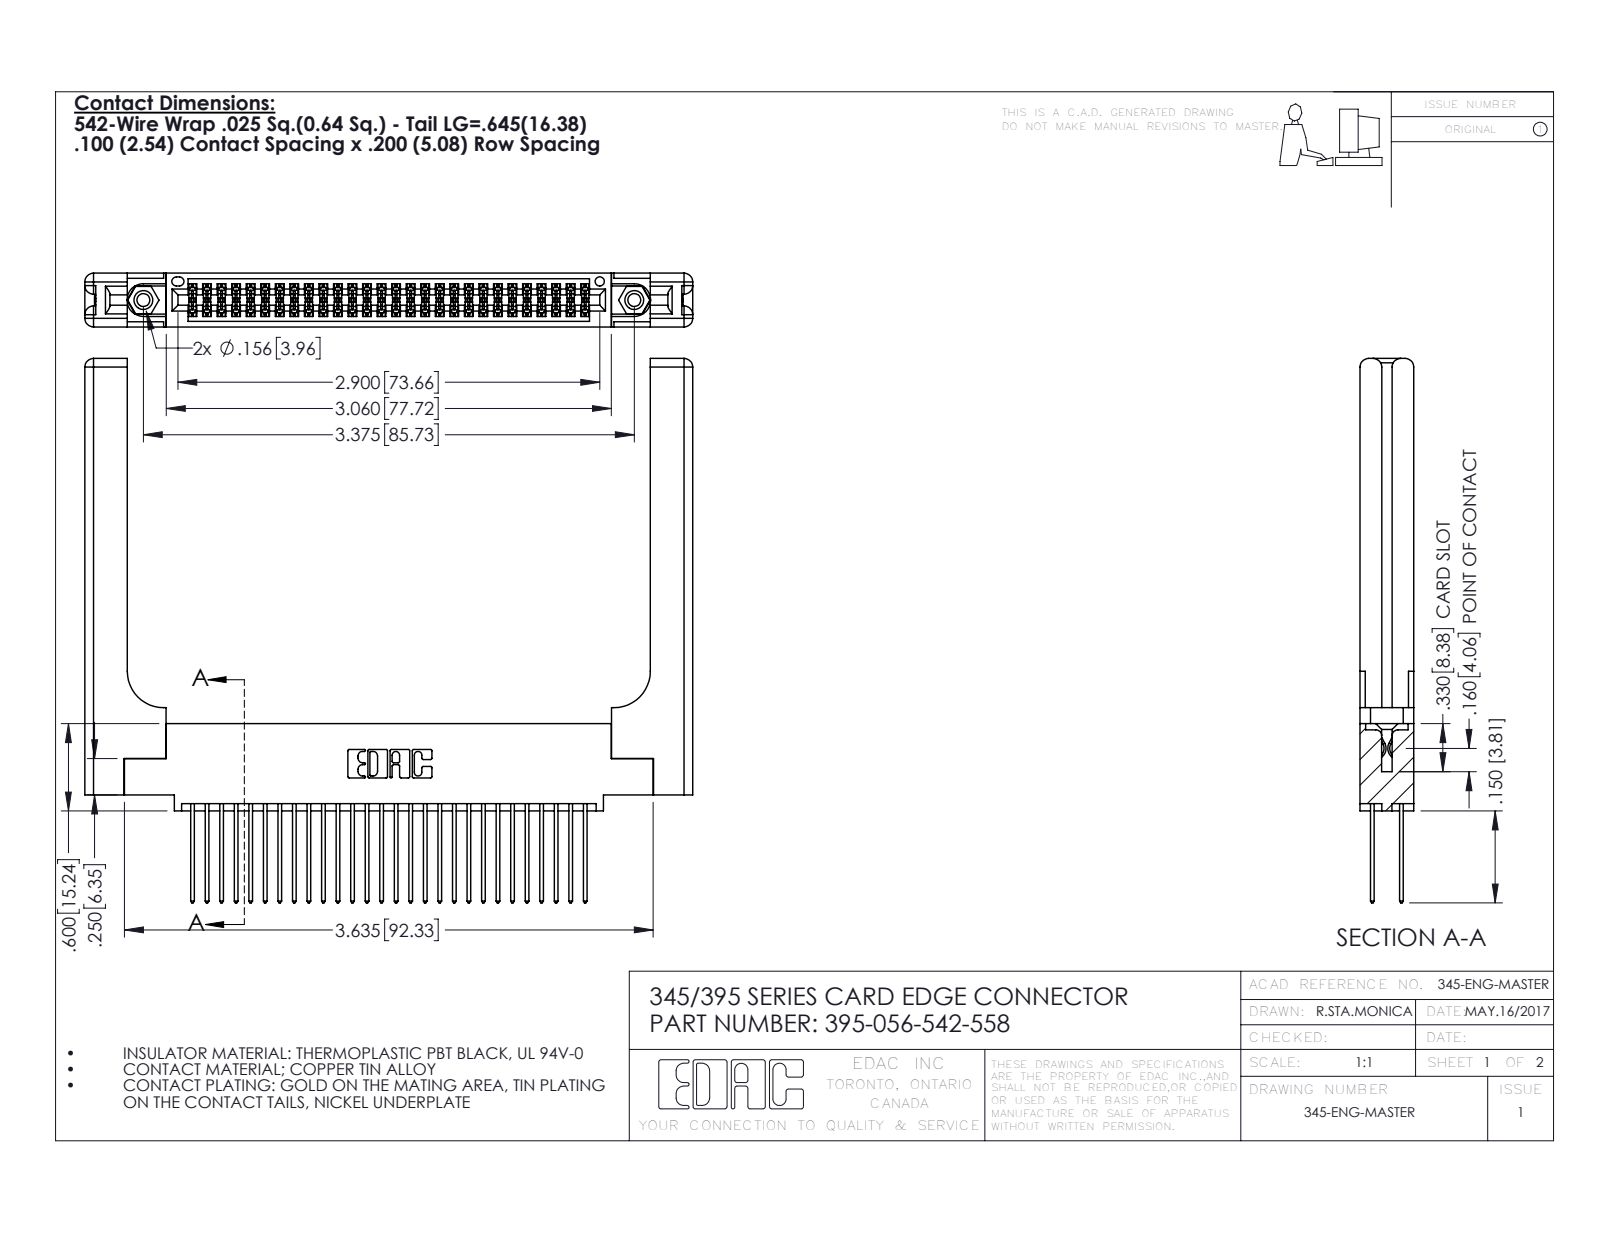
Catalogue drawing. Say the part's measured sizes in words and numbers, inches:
The part is named "345-250-001_345-250-001-102; 395-056-542-558; 345 Part_0.110 Offset - 0.156 Dia-TH; 345-292-001_345-293-142 (+1 more)". Its 3-D file was written by "SolidWorks 2016 (CONFIG_CONTROL_DESIGN)". It is 61 solids with 3186 faces: 2080 planar, 1046 cylindrical and 60 other. Overall it measures 4.179 by 3.742 by 0.37 inches. Its volume is 1.15 cubic inches and its surface area 33.21 square inches. Round holes: 2 of diameter 0.089, 2 of diameter 0.125, 2 of diameter 0.156, 1 of diameter 0.064. Round bosses or shafts: 2 of diameter 0.155. Partial cylindrical surfaces (rounded edges, fillets, slot ends): 84 of radius 0.006, 56 of radius 0.01, 22 of radius 0.01, 16 of radius 0.06, 6 of radius 0.007, 6 of radius 0.031, 3 of radius 0.026, 2 of radius 0.014. The main face-to-face distances are 0.072, 0.298, 0.37, 0.098, 0.272, 0.025, 0.2, 0.225, 0.148, 0.15. The hole center spacings are 0.27, 3.14, 3.375.
